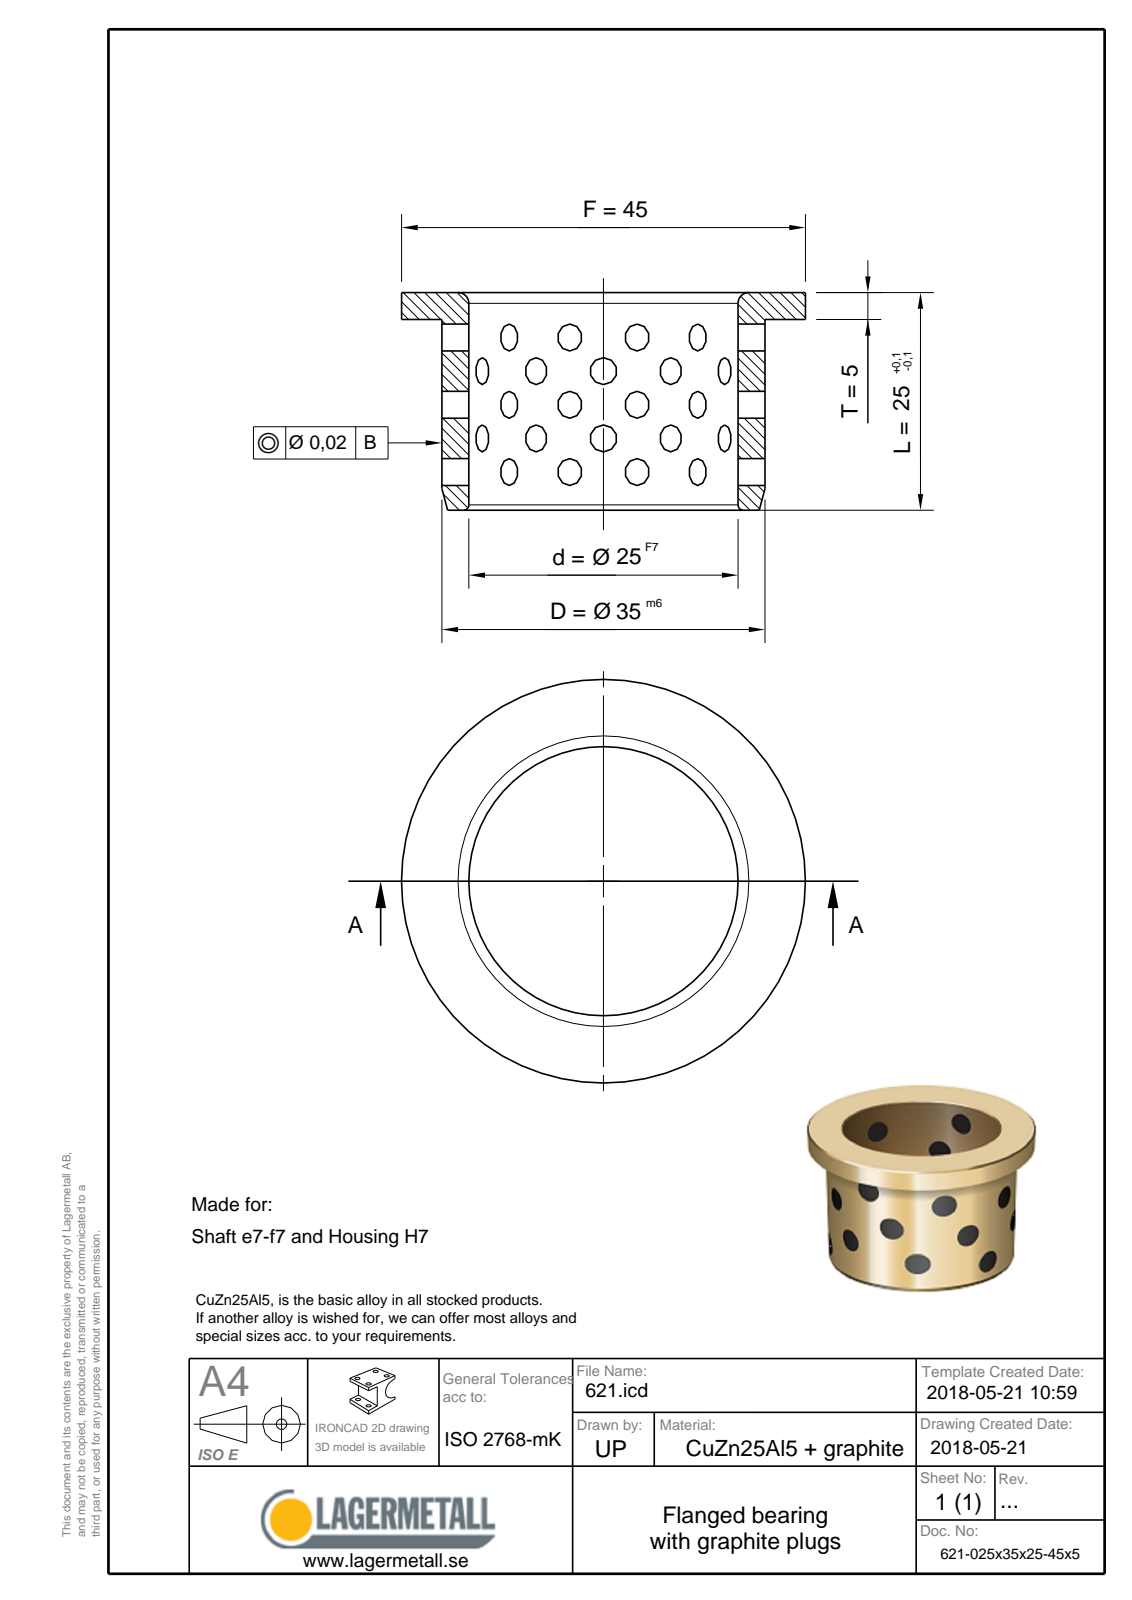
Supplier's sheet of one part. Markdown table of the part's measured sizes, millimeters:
| quantity | value |
| --- | --- |
| part name | 621-025x35x25-45x5 |
| STEP written by | Spatial InterOp 3D (CONFIG_CONTROL_DESIGN) |
| units | millimeters |
| bodies | 1 solid, 9 faces (3 planar, 3 cylindrical, 3 other) |
| overall size | 45 × 45 × 25 |
| volume | 14 746 mm³ |
| surface area | 6 874 mm² |
| round holes (diameter × count) | 25 × 1 |
| round bosses / shafts (diameter × count) | 45 × 1, 35 × 1 |
| main face-to-face distances | 5, 20, 25 |
